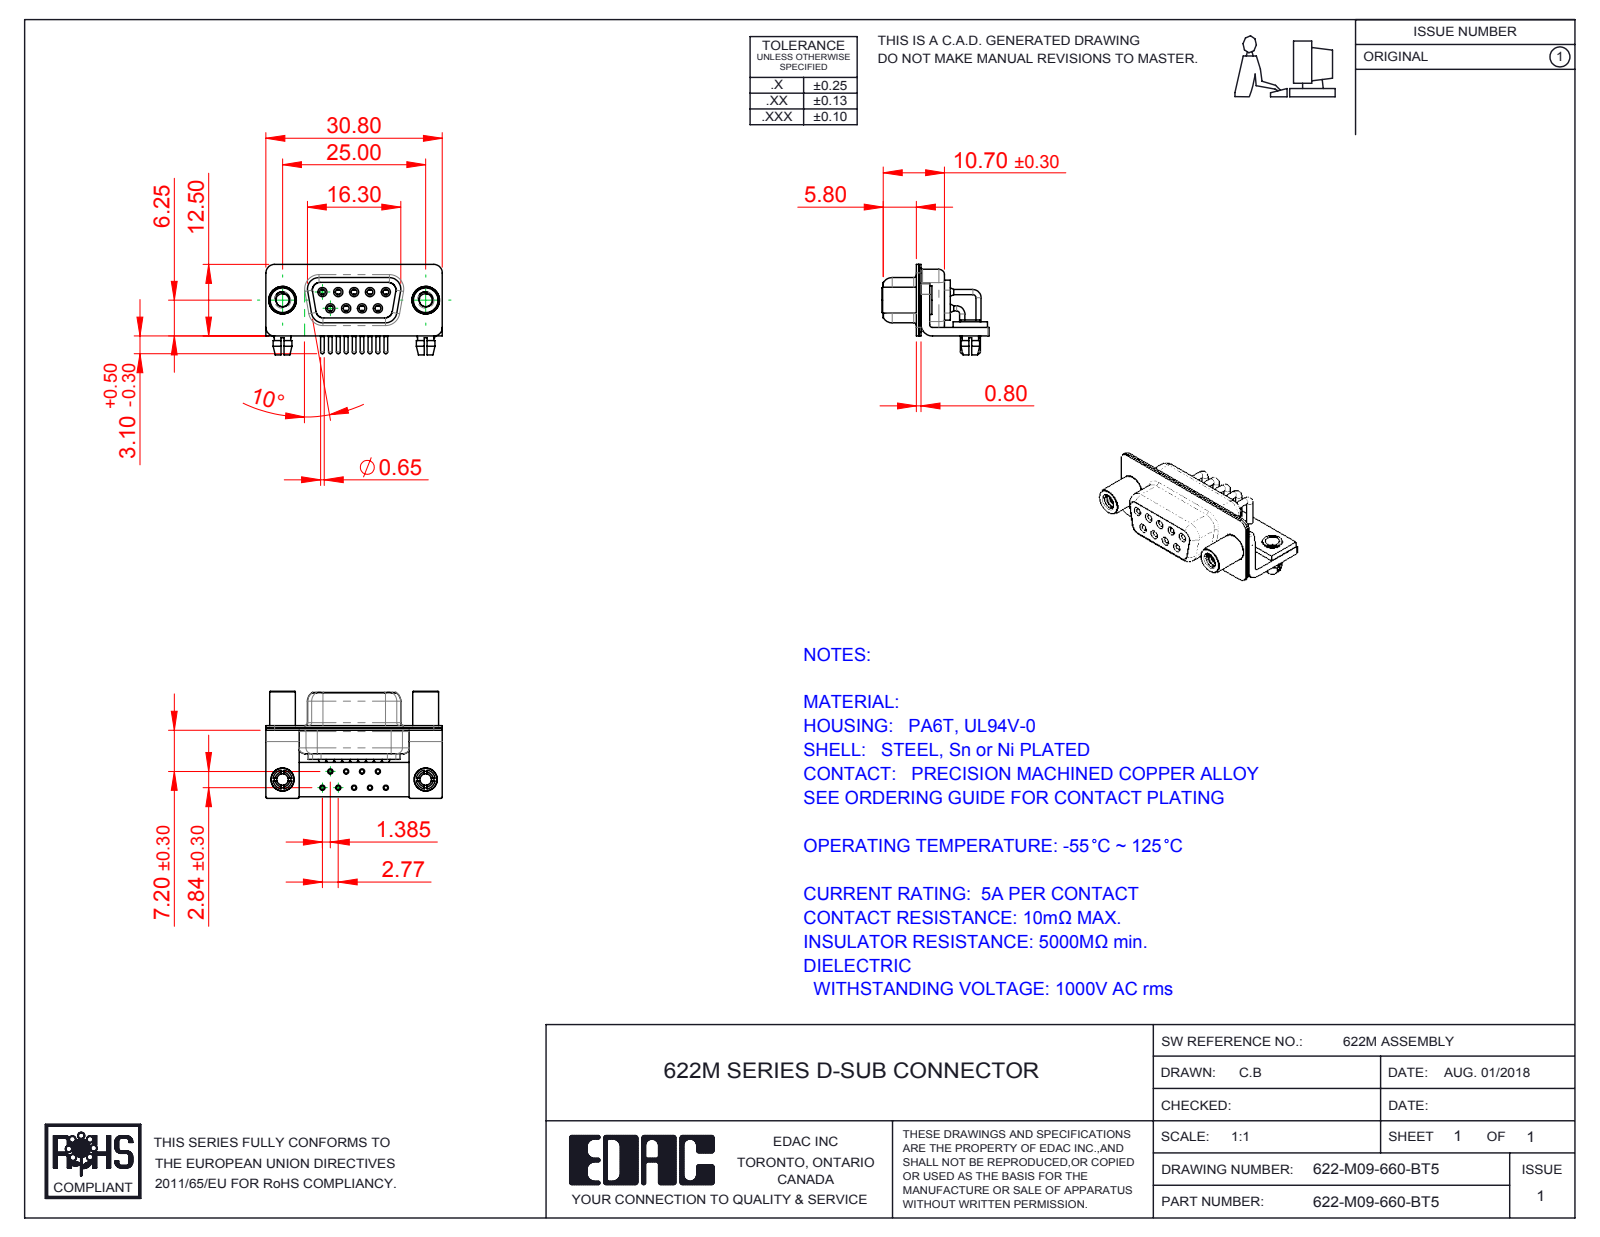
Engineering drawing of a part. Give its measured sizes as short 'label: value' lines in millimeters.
name: 622M Housing_09 Contacts; 622-M09-660-BT5; 622M Board Lock; 622M Stabilizer Board_09 Contacts (+6 more)
written by: SolidWorks 2016 (CONFIG_CONTROL_DESIGN)
unit: mm
bodies: 19 solids, 966 faces (278 planar, 458 cylindrical, 230 other)
size: 30.8 × 18.7 × 15.8
volume: 2 304 mm³; area: 6 084 mm²
holes: 11× ⌀2, 9× ⌀0.9, 9× ⌀1, 9× ⌀1.1, 9× ⌀1.7, 9× ⌀1.8, 2× ⌀2.26, 2× ⌀2.5, 2× ⌀3.2, 2× ⌀4, 2× ⌀4.8
bosses: 9× ⌀1.6, 9× ⌀1.5, 9× ⌀0.9, 9× ⌀0.65, 2× ⌀5, 2× ⌀4.9, 2× ⌀4.5, 2× ⌀4
rounds: 16× R0.25, 16× R1.5, 13× R2, 8× R1.35, 8× R1.6, 5× R0.5, 4× R0.6, 4× R0.65
face distances: 0.4, 0.8, 2.3, 1.5, 1.9, 1, 9.35, 1.45, 8.5, 8.95
hole spacings: 3.16, 2.77, 5.54, 5.03, 5.04, 8.31, 7.48, 7.49
